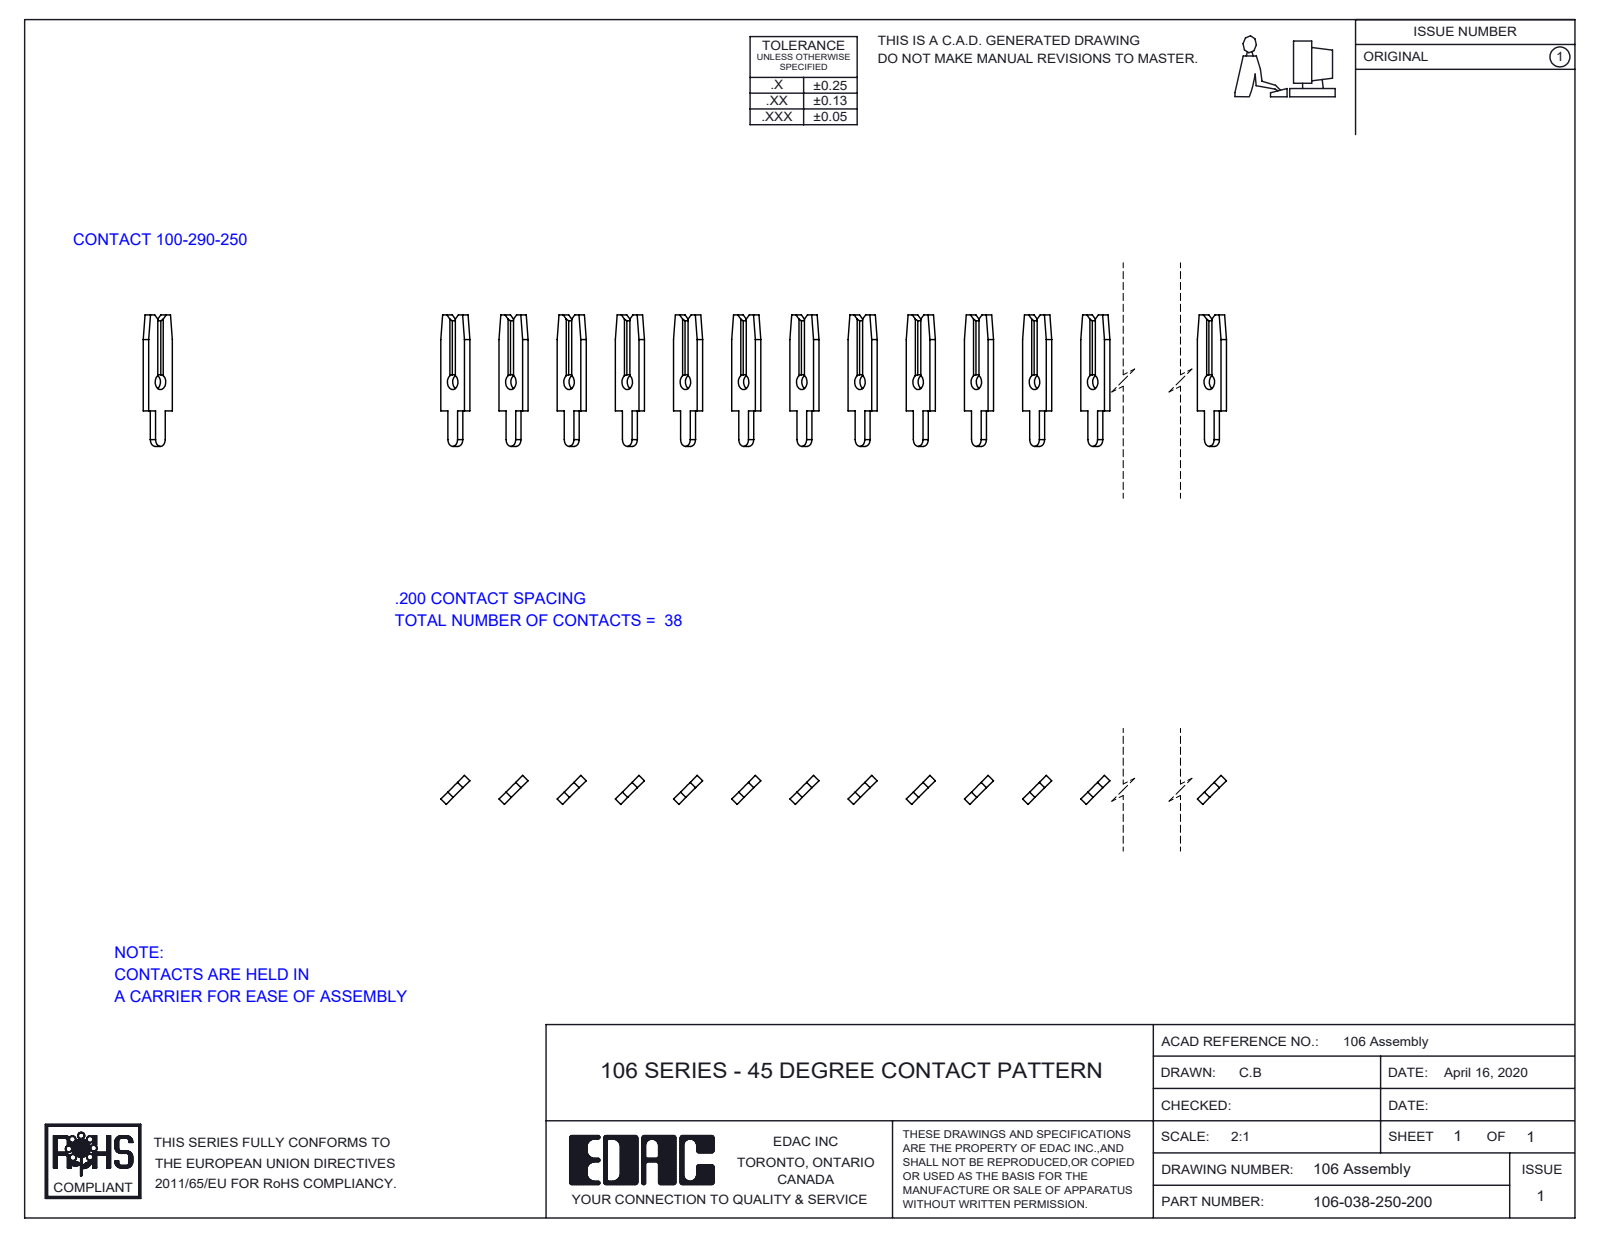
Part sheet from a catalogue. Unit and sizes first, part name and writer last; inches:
Units: inches
Overall size (bounding box): 7.5 × 0.452 × 0.1
Round holes (diameter × count): ⌀0.052 ×38
Partial cylindrical surfaces — rounded edges, fillets, slot ends (radius × count): R0.024 ×38
Main face-to-face distances: 0.141, 0.848, 0.707, 0.283, 0.99, 0.566, 0.424, 1.131, 0.424, 1.556
Hole centre spacings: 0.141, 0.283, 0.424, 0.848, 1.839, 0.99, 1.556, 1.697
Volume: 0.036 in³ · Surface area: 4.32 in²
Bodies: 38 solids, 912 faces (760 planar, 152 cylindrical, 0 other)
Part name (STEP PRODUCT): 100-290-001_100-290-250; 106-038-250-200
STEP written by: SolidWorks 2016 (CONFIG_CONTROL_DESIGN)
